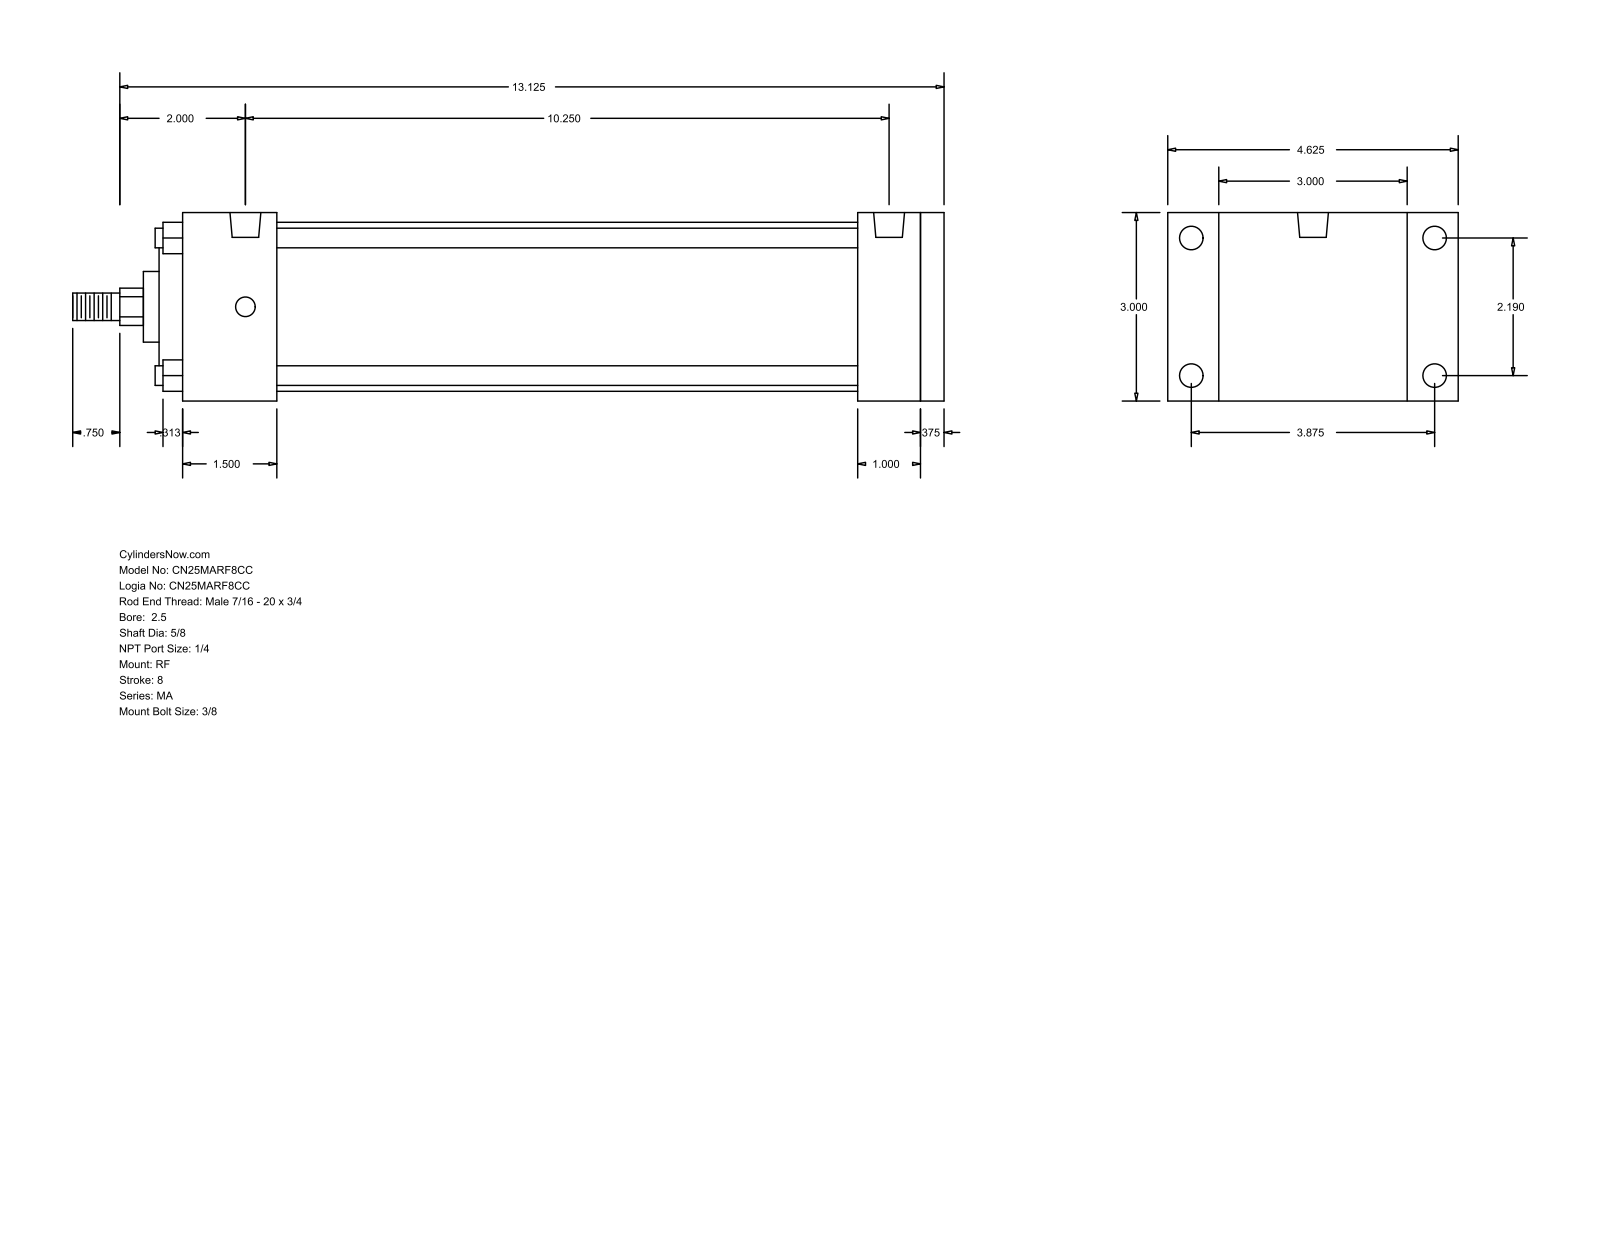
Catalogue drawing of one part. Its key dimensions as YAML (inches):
part_name: "MA_RF__0250_0.625"
step_written_by: "GSSL Pune (CONFIG_CONTROL_DESIGN)"
units: inches
bodies: {solids: 0, faces: 94, planar: 65, cylindrical: 29, other: 0}
overall_size: [13.875, 4.625, 3]
round_holes:
  - {diameter: 0.313, count: 4}
  - {diameter: 0.375, count: 4}
  - {diameter: 0.492, count: 2}
round_bosses_or_shafts:
  - {diameter: 0.313, count: 4}
  - {diameter: 2.69, count: 1}
  - {diameter: 2, count: 1}
  - {diameter: 1.125, count: 1}
  - {diameter: 0.625, count: 1}
  - {diameter: 0.437, count: 1}
partial_cylinders:
  - {radius: 0.297, count: 1}
face_to_face_distances: [3, 12.125, 0.375, 11.75, 1, 1.375, 1.5, 10.75, 9.25, 10.25]
hole_center_spacings: [2.19, 3.875, 4.451, 10.25]
